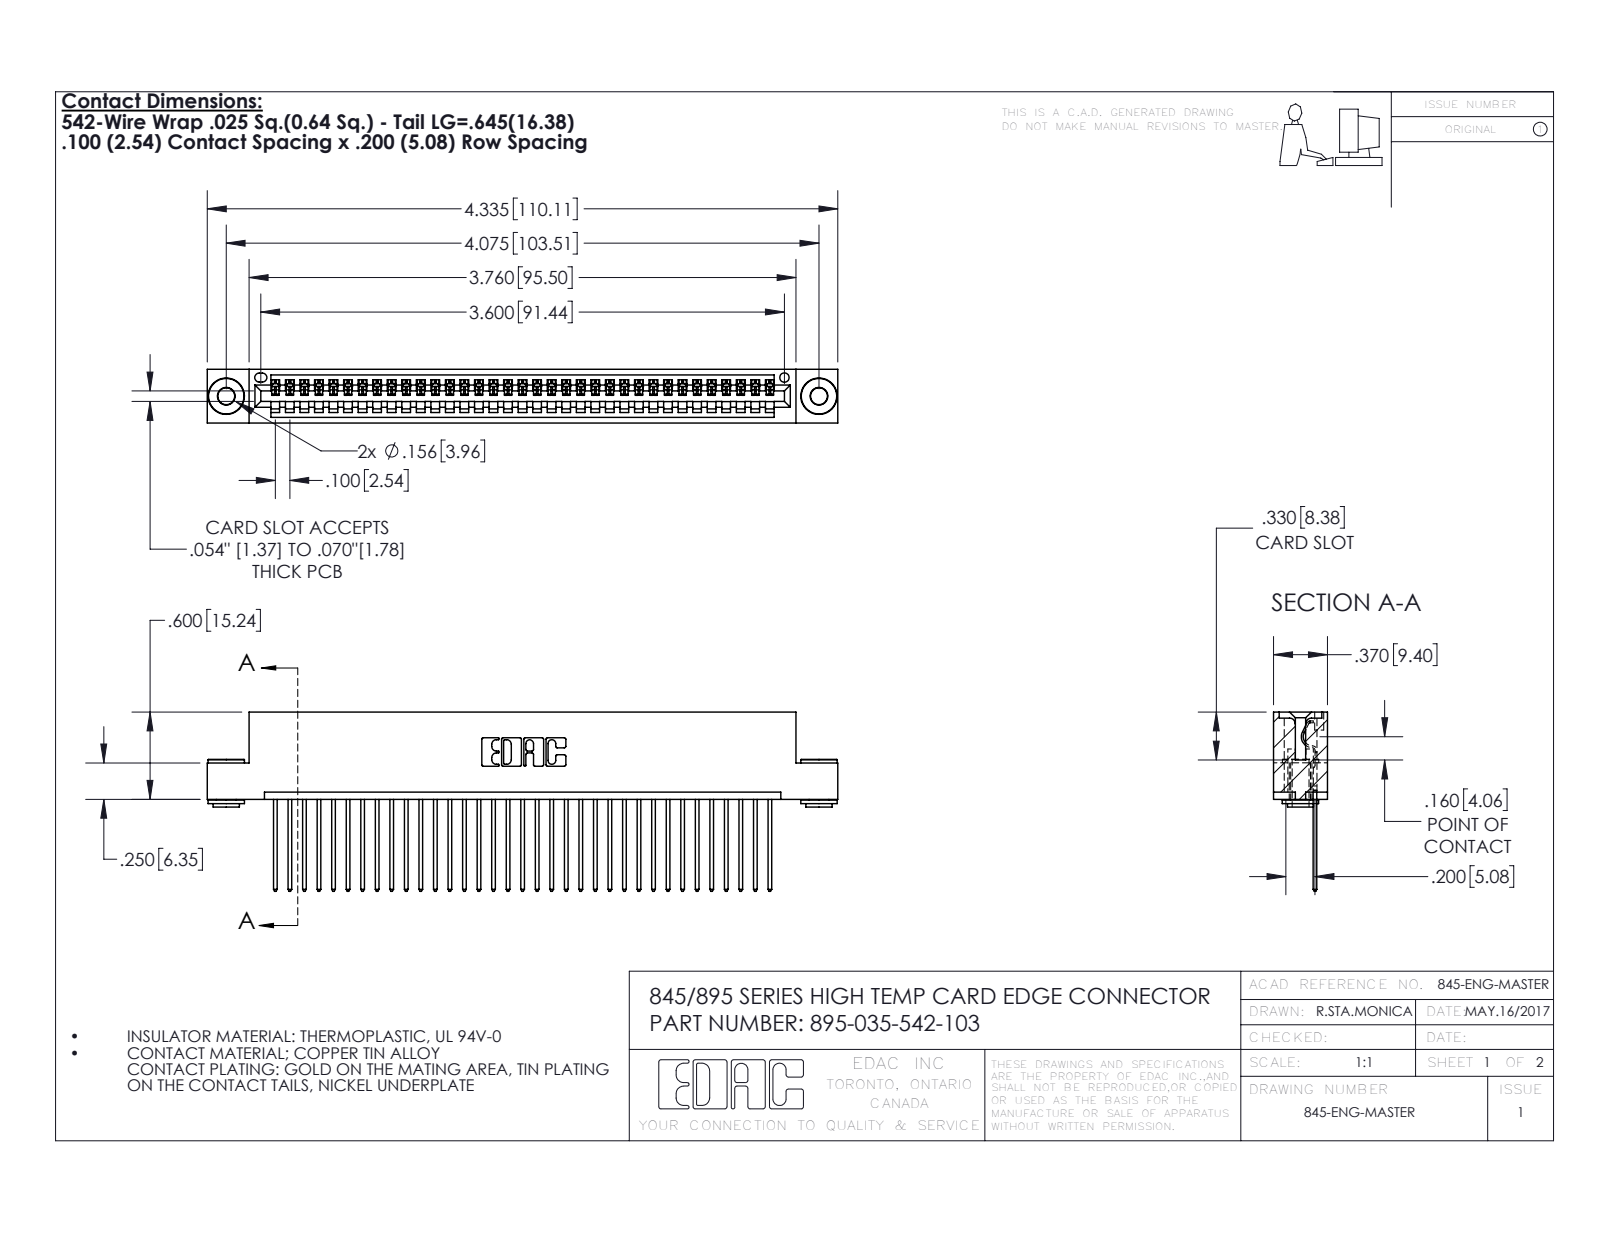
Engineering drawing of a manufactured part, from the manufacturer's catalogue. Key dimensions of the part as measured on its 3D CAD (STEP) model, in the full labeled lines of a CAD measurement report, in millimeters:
Part name (STEP PRODUCT): 395-035-542-103; 345-250-002_345-250-002-102; 345 Part_Flush Mounting Lugs - 0.156 Dia-TH; 345-292-001_345-293-142
STEP written by: SolidWorks 2016 (CONFIG_CONTROL_DESIGN)
Units: millimetres
Bodies: 38 solids, 2194 faces (1490 planar, 696 cylindrical, 8 other)
Overall size (bounding box): 110.1 × 31.3 × 9.4
Volume: 10 500 mm³ · Surface area: 14 560 mm²
Round holes (diameter × count): ⌀2.9 ×2, ⌀4 ×2, ⌀1.6 ×1
Round bosses / shafts (diameter × count): ⌀6.4 ×2, ⌀4.6 ×2, ⌀3.5 ×2
Partial cylindrical surfaces — rounded edges, fillets, slot ends (radius × count): R0.2 ×70, R0.3 ×70, R0.3 ×22, R0.2 ×6, R0.8 ×6, R0.7 ×3, R0.8 ×2, R1 ×2
Main face-to-face distances: 1.8, 7.6, 0.6, 9.4, 2.5, 6.9, 5.1, 5.7, 3.8, 1.8
Hole centre spacings: 6.9, 97.5, 103.5
